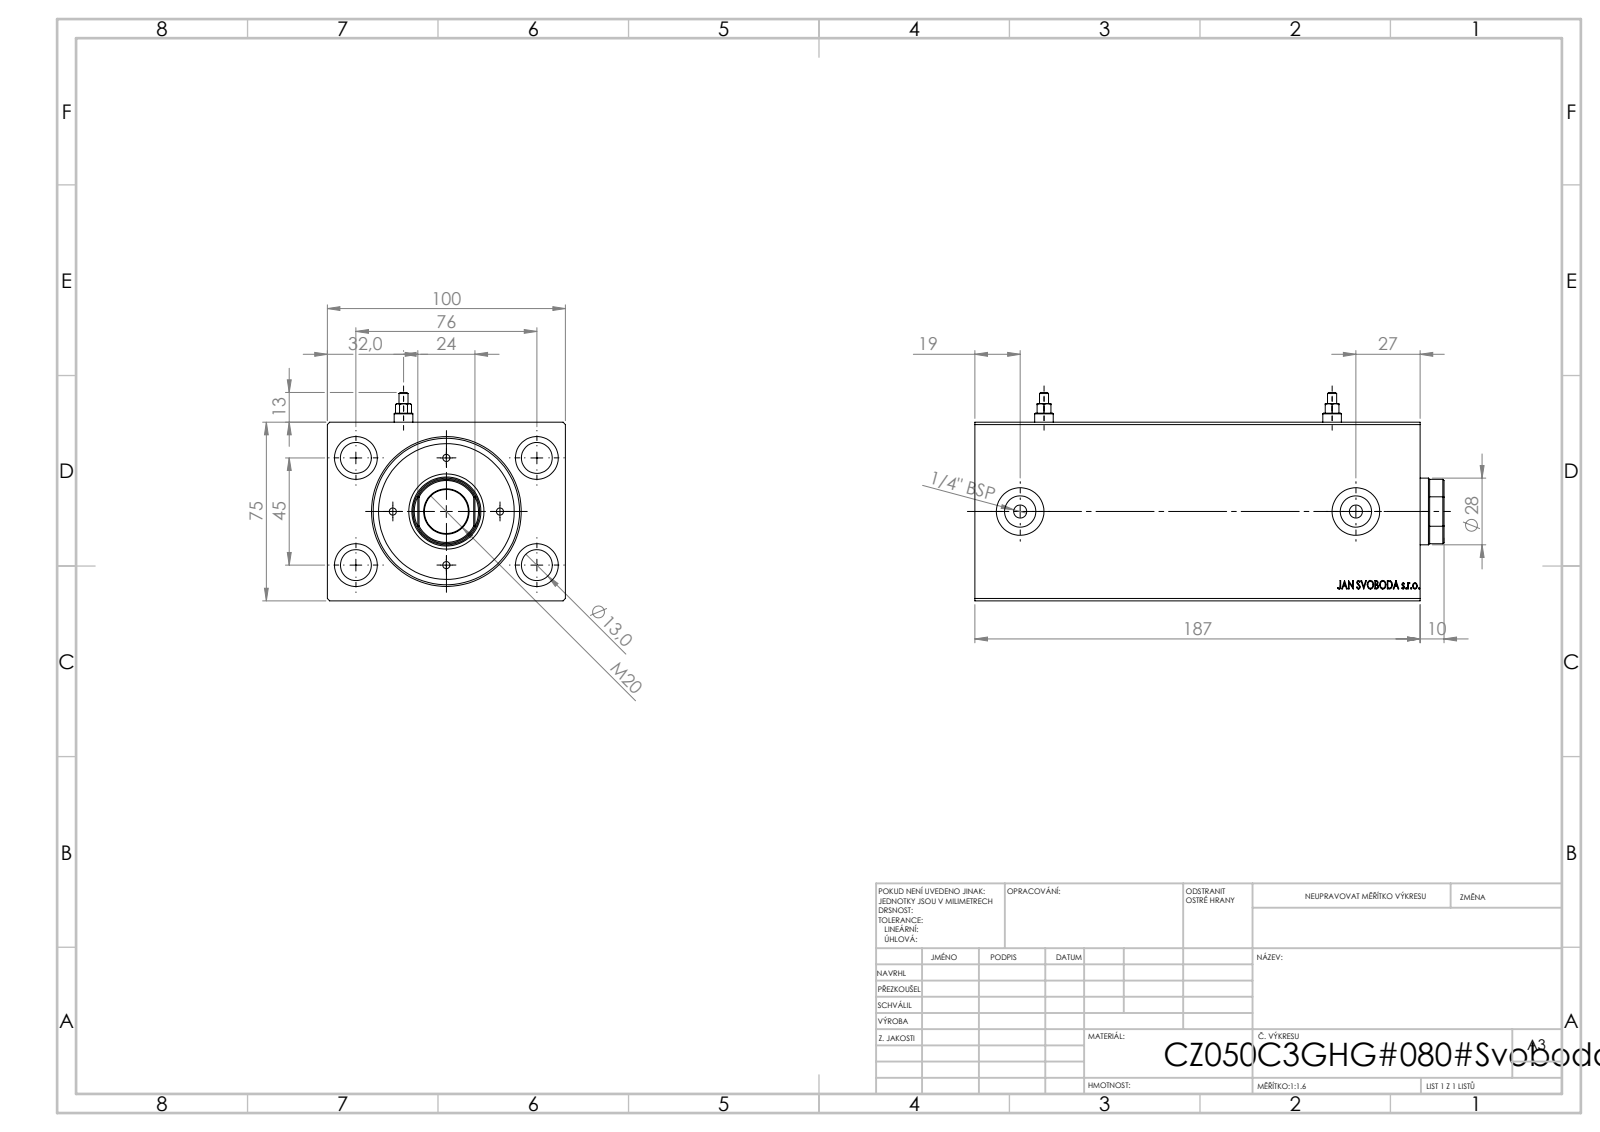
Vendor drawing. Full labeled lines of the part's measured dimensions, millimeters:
STEP written by: SolidWorks 2019 (CONFIG_CONTROL_DESIGN)
Units: millimetres
Bodies: 1 solid, 825 faces (397 planar, 46 cylindrical, 382 other)
Overall size (bounding box): 187 × 100 × 75
Volume: 946 056 mm³ · Surface area: 139 247 mm²
Round holes (diameter × count): ⌀13 ×4, ⌀18 ×4, ⌀5.5 ×2, ⌀8 ×2, ⌀13.16 ×2, ⌀20 ×2, ⌀36 ×1, ⌀50 ×1, ⌀61.5 ×1
Main face-to-face distances: 75, 100, 187, 169.2, 17.8, 186.8, 17.6, 10, 159.2, 176.8
Hole centre spacings: 44.16, 45, 76, 88.32, 121, 141
